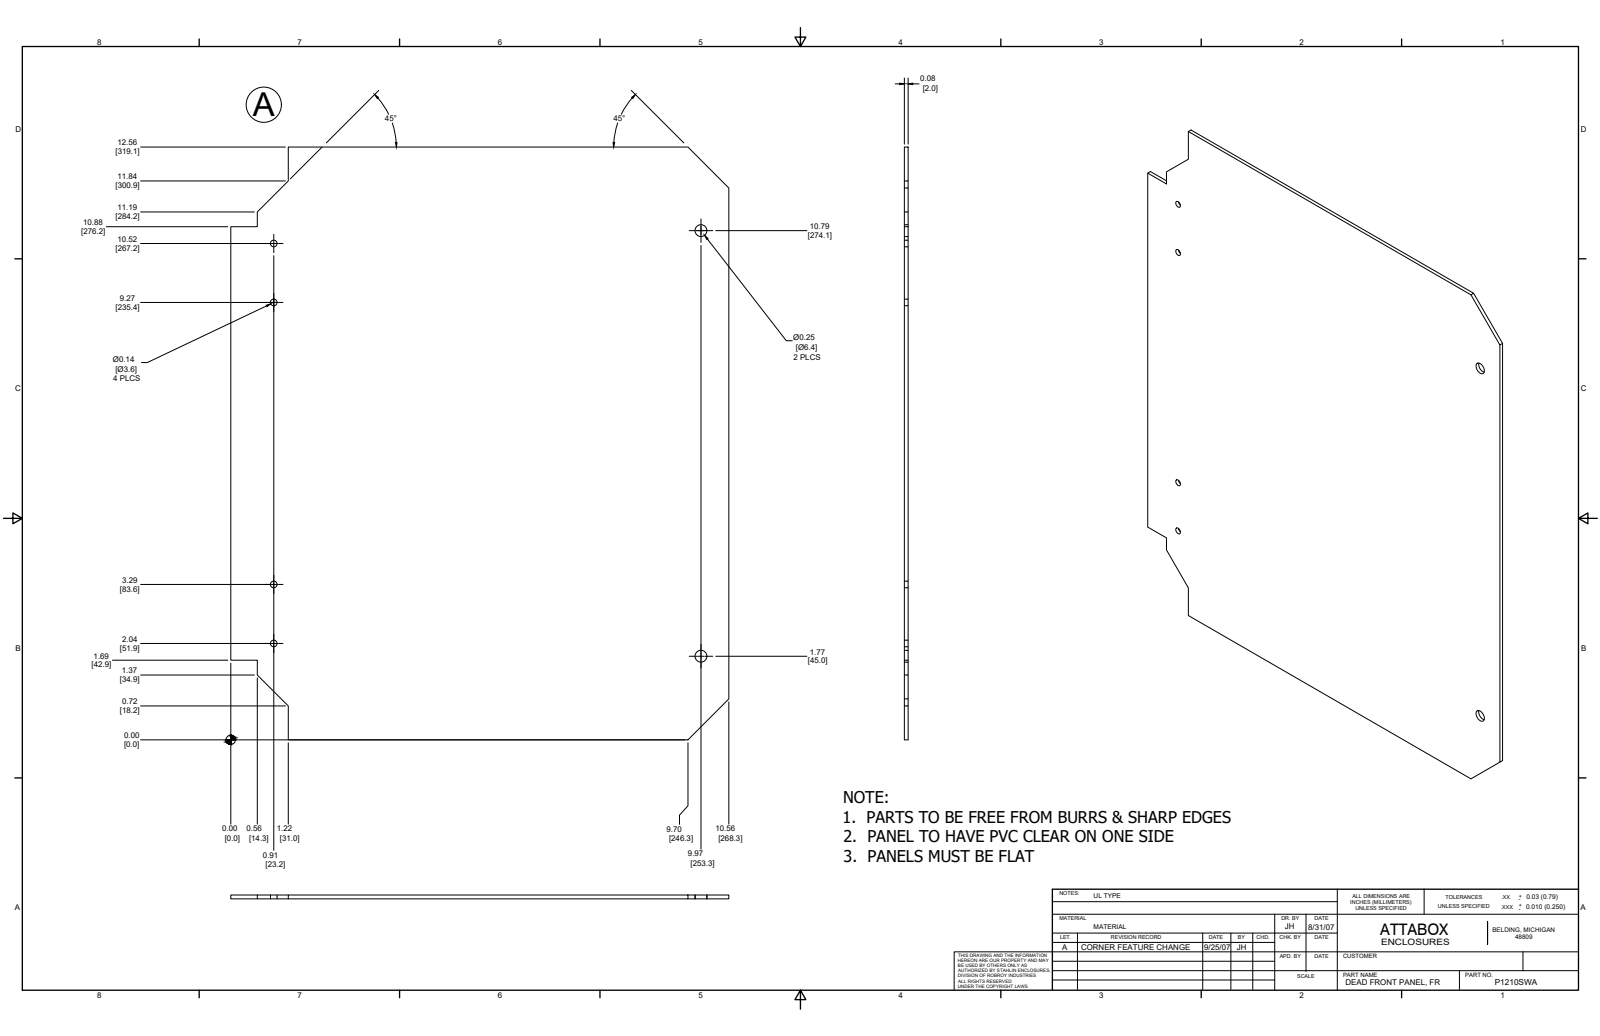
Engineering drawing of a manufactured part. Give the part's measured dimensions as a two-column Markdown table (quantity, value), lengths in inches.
| quantity | value |
| --- | --- |
| part name | P1210SWAL |
| STEP written by | Autodesk Inventor 11 (AUTOMOTIVE_DESIGN) |
| units | inches |
| bodies | 1 solid, 20 faces (14 planar, 6 cylindrical, 0 other) |
| overall size | 12.563 × 10.563 × 0.08 |
| volume | 10.37 in³ |
| surface area | 263 in² |
| round holes (diameter × count) | 0.14 × 4, 0.25 × 2 |
| main face-to-face distances | 0.08, 10.562, 12.562, 1.09, 11.472, 9.472, 14.499, 10.383 |
| hole center spacings | 1.25, 7.226, 9.064, 9.187, 11.76, 12.593, 5.976, 8.476 |
